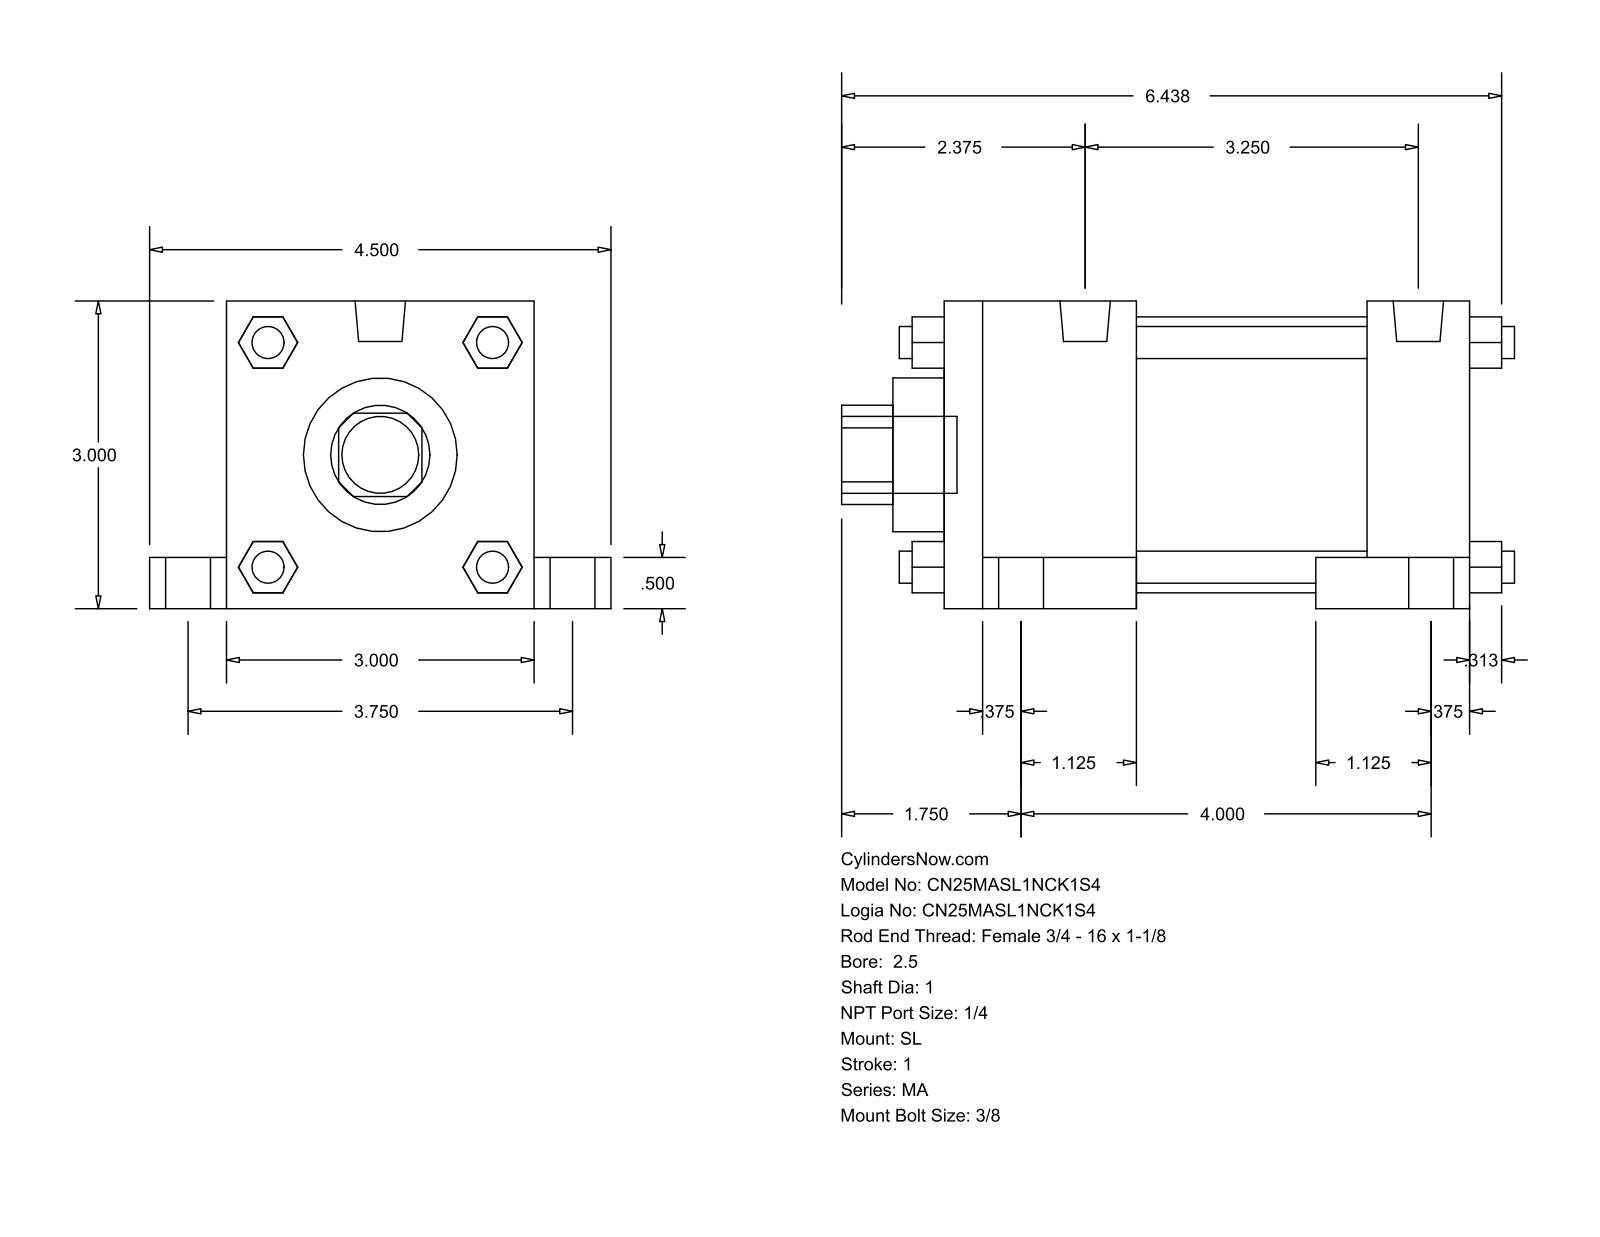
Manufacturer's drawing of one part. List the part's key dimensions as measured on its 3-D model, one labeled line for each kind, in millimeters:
Part name (STEP PRODUCT): MA_SL__0250_1
STEP written by: GSSL Pune (CONFIG_CONTROL_DESIGN)
Units: millimetres
Bodies: 0 solids, 148 faces (112 planar, 36 cylindrical, 0 other)
Overall size (bounding box): 166.69 × 114.3 × 76.2
Round holes (diameter × count): ⌀25.4 ×1, ⌀38.1 ×1, ⌀68.33 ×1
Round bosses / shafts (diameter × count): ⌀7.94 ×8, ⌀17.46 ×4, ⌀11.11 ×4, ⌀12.49 ×2, ⌀19.05 ×1
Partial cylindrical surfaces — rounded edges, fillets, slot ends (radius × count): R12.29 ×1
Main face-to-face distances: 76.2, 130.17, 12.7, 57.15, 25.39, 47.63, 82.54, 104.78, 19.05, 95.25
